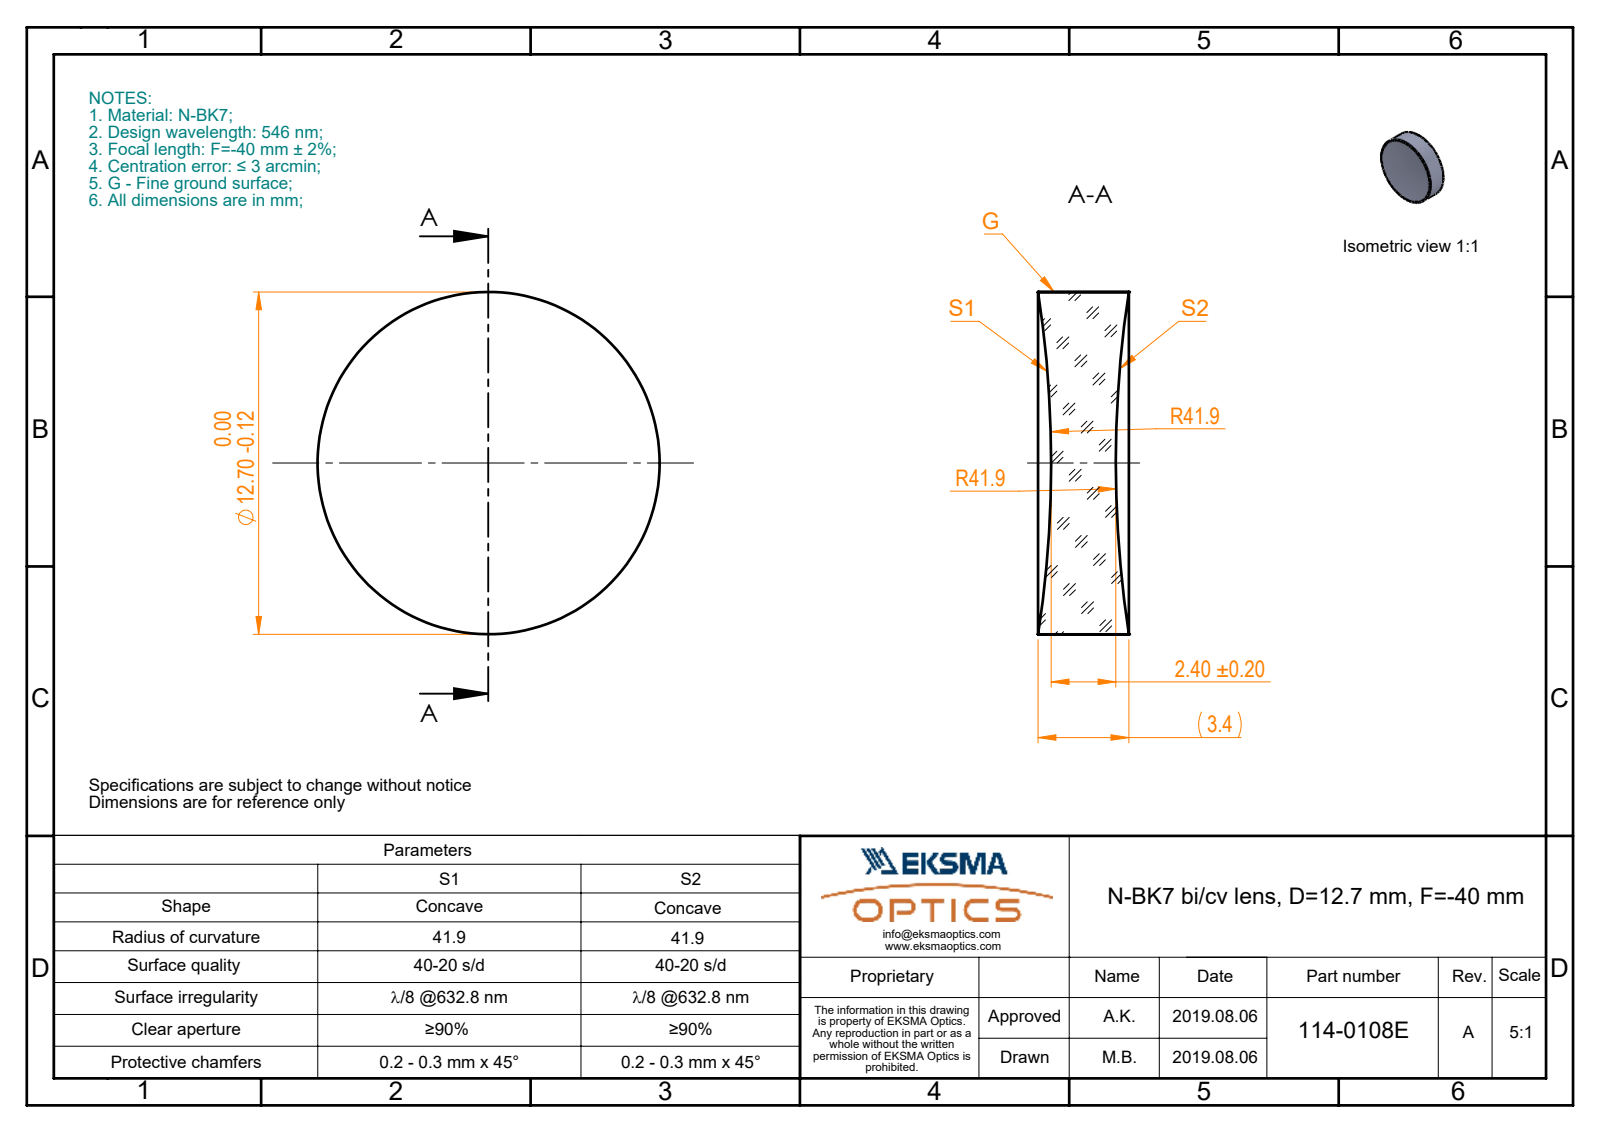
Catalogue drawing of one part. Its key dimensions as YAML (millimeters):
part_name: "114-0108E BK7 bi-cv 12.7 F-40"
step_written_by: "SolidWorks 2017 (CONFIG_CONTROL_DESIGN)"
units: millimeters
bodies: {solids: 1, faces: 6, planar: 0, cylindrical: 2, other: 4}
overall_size: [12.7, 12.7, 3.37]
volume: 365
surface_area: 389
round_bosses_or_shafts:
  - {diameter: 12.7, count: 1}
